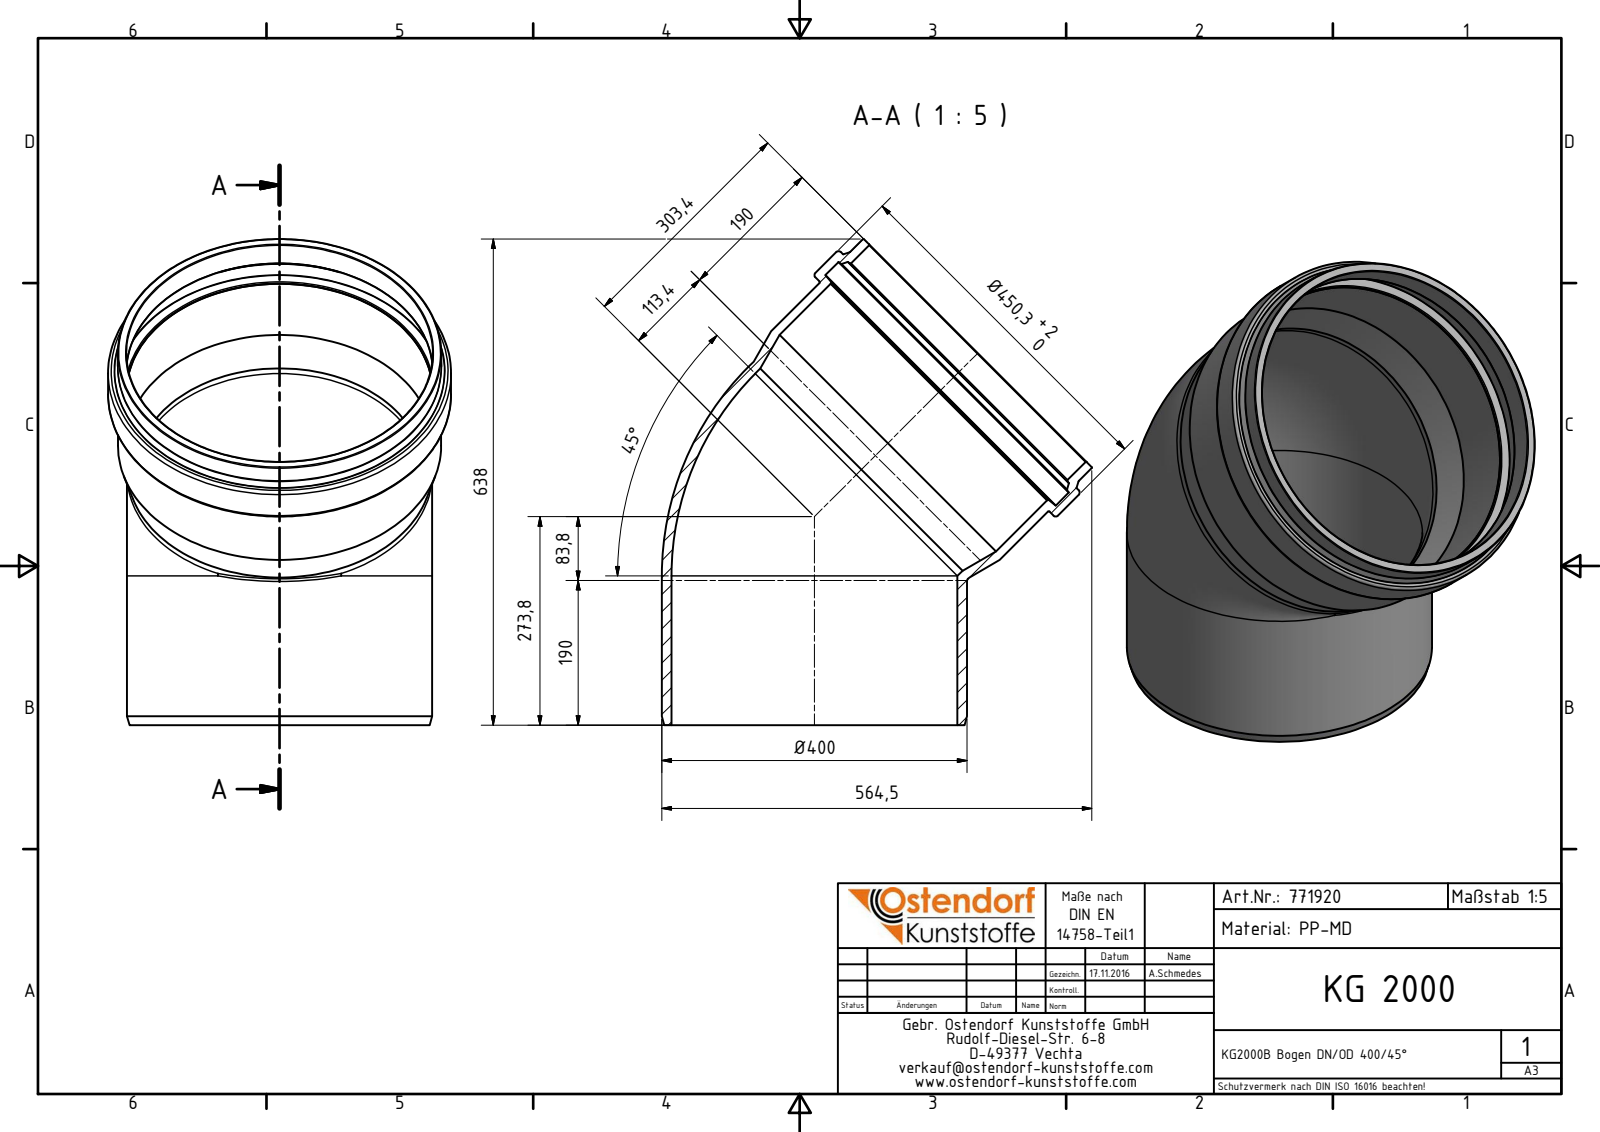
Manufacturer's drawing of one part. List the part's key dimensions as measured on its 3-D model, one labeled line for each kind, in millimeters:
Part name (STEP PRODUCT): 771920 KG2000B Bogen DN_OD 400_45°
STEP written by: Autodesk Inventor 2016 (AUTOMOTIVE_DESIGN)
Units: millimetres
Bodies: 1 solid, 40 faces (5 planar, 11 cylindrical, 24 other)
Overall size (bounding box): 638 × 564.5 × 450.3
Volume: 8 347 000 mm³ · Surface area: 1 504 000 mm²
Round holes (diameter × count): ⌀375.5 ×2, ⌀402.1 ×2, ⌀401.7 ×1, ⌀427.7 ×1
Round bosses / shafts (diameter × count): ⌀400.5 ×2, ⌀450.3 ×1, ⌀424.7 ×1, ⌀424.3 ×1
Main face-to-face distances: 80.39, 46.99, 33.4, 8.14, 38.85, 72.25
